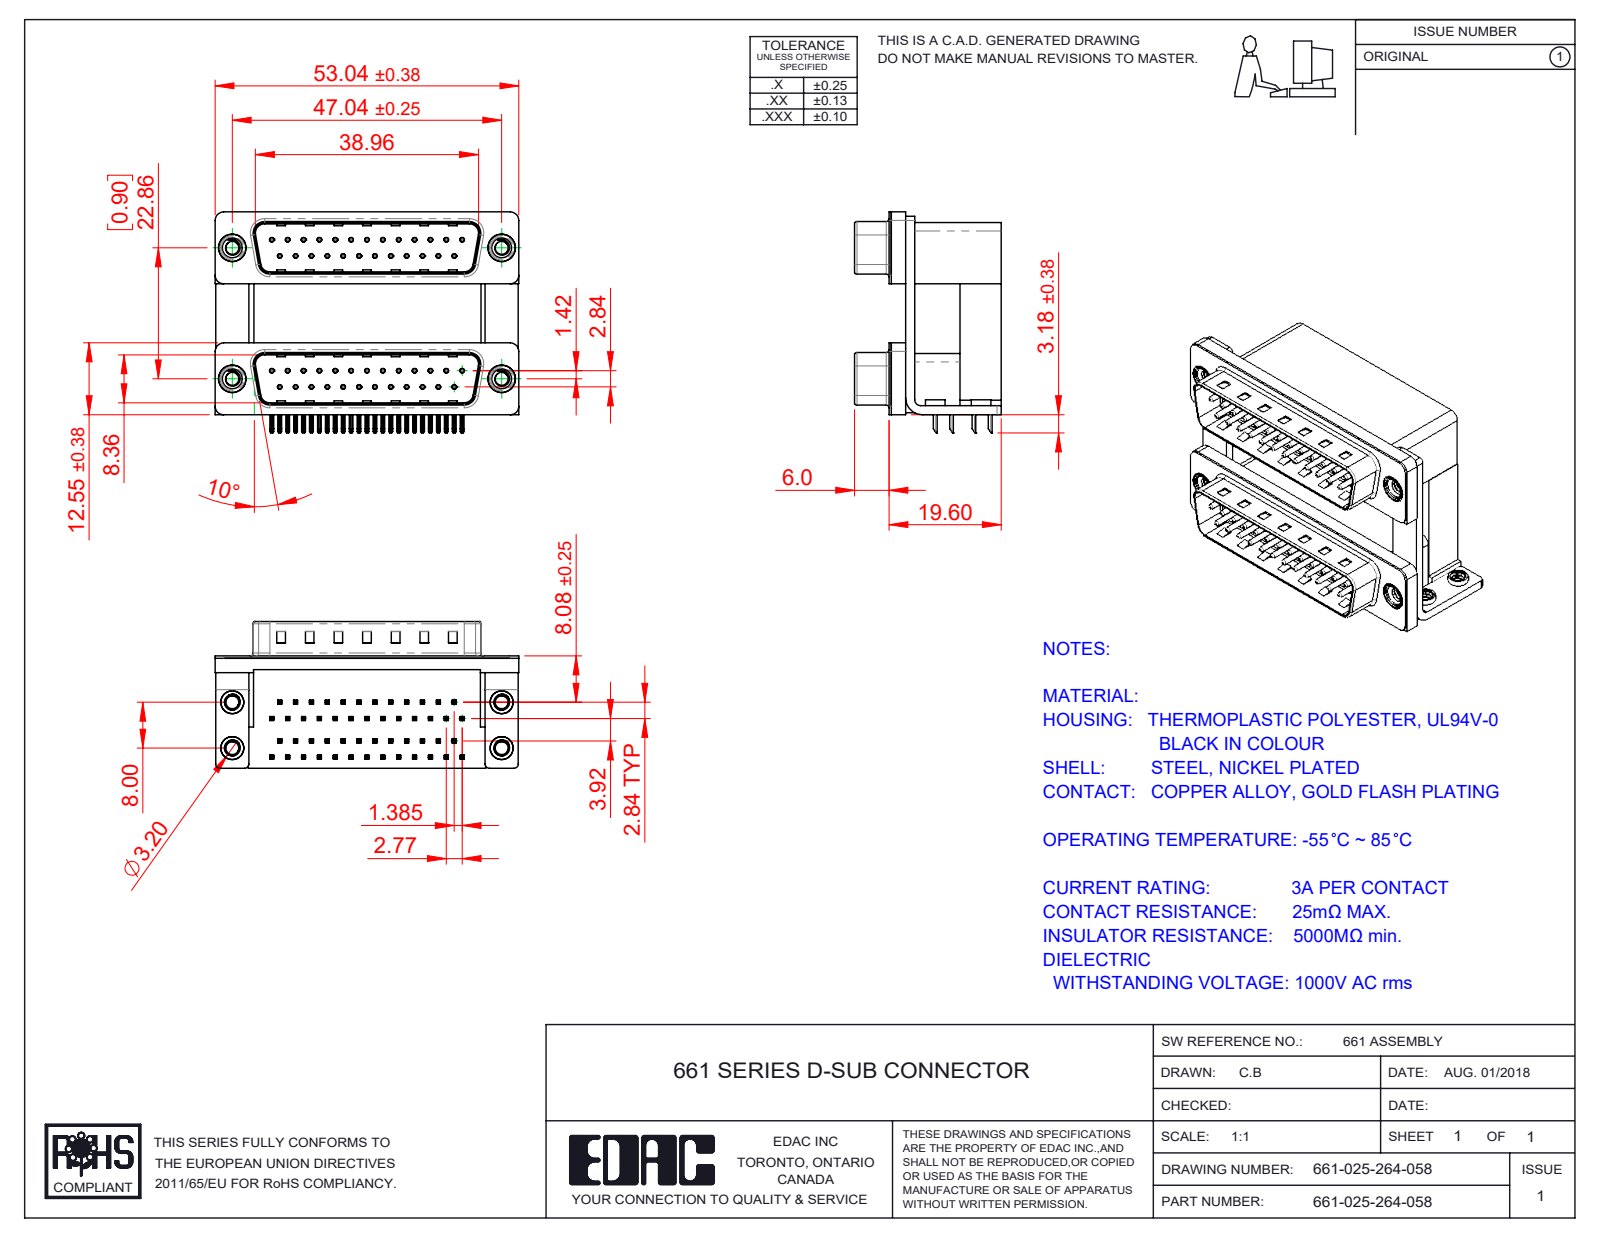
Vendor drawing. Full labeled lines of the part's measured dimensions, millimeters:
Part name (STEP PRODUCT): 661 Housing Upper_25 Contacts H; 661 Mounting Bracket_ThruH; 661 4-40 Threaded Board Mount; 661 Shell_25 Contacts (+8 more)
STEP written by: SolidWorks 2020 (CONFIG_CONTROL_DESIGN)
Units: millimetres
Bodies: 65 solids, 4754 faces (2950 planar, 1358 cylindrical, 446 other)
Overall size (bounding box): 53.04 × 38.59 × 25.6
Volume: 22 396 mm³ · Surface area: 23 398 mm²
Round holes (diameter × count): ⌀0.35 ×50, ⌀0.8 ×50, ⌀2.26 ×8, ⌀2.75 ×4, ⌀3.2 ×4, ⌀3.5 ×4, ⌀4 ×4, ⌀4.8 ×4, ⌀5 ×4
Round bosses / shafts (diameter × count): ⌀0.75 ×50, ⌀4.9 ×4, ⌀4.75 ×4, ⌀4 ×4, ⌀3.9 ×4, ⌀3.4 ×4
Partial cylindrical surfaces — rounded edges, fillets, slot ends (radius × count): R0.25 ×200, R0.12 ×100, R0.5 ×16, R1.5 ×14, R0.75 ×8, R0.9 ×8, R1.6 ×8, R2 ×8
Main face-to-face distances: 12, 22.86, 19.2, 0.4, 7.2, 10.7, 12.4, 16.7, 9.5, 2.5
Hole centre spacings: 2.77, 3.16, 5.54, 8.31, 11.08, 13.85, 16.62, 5.03
